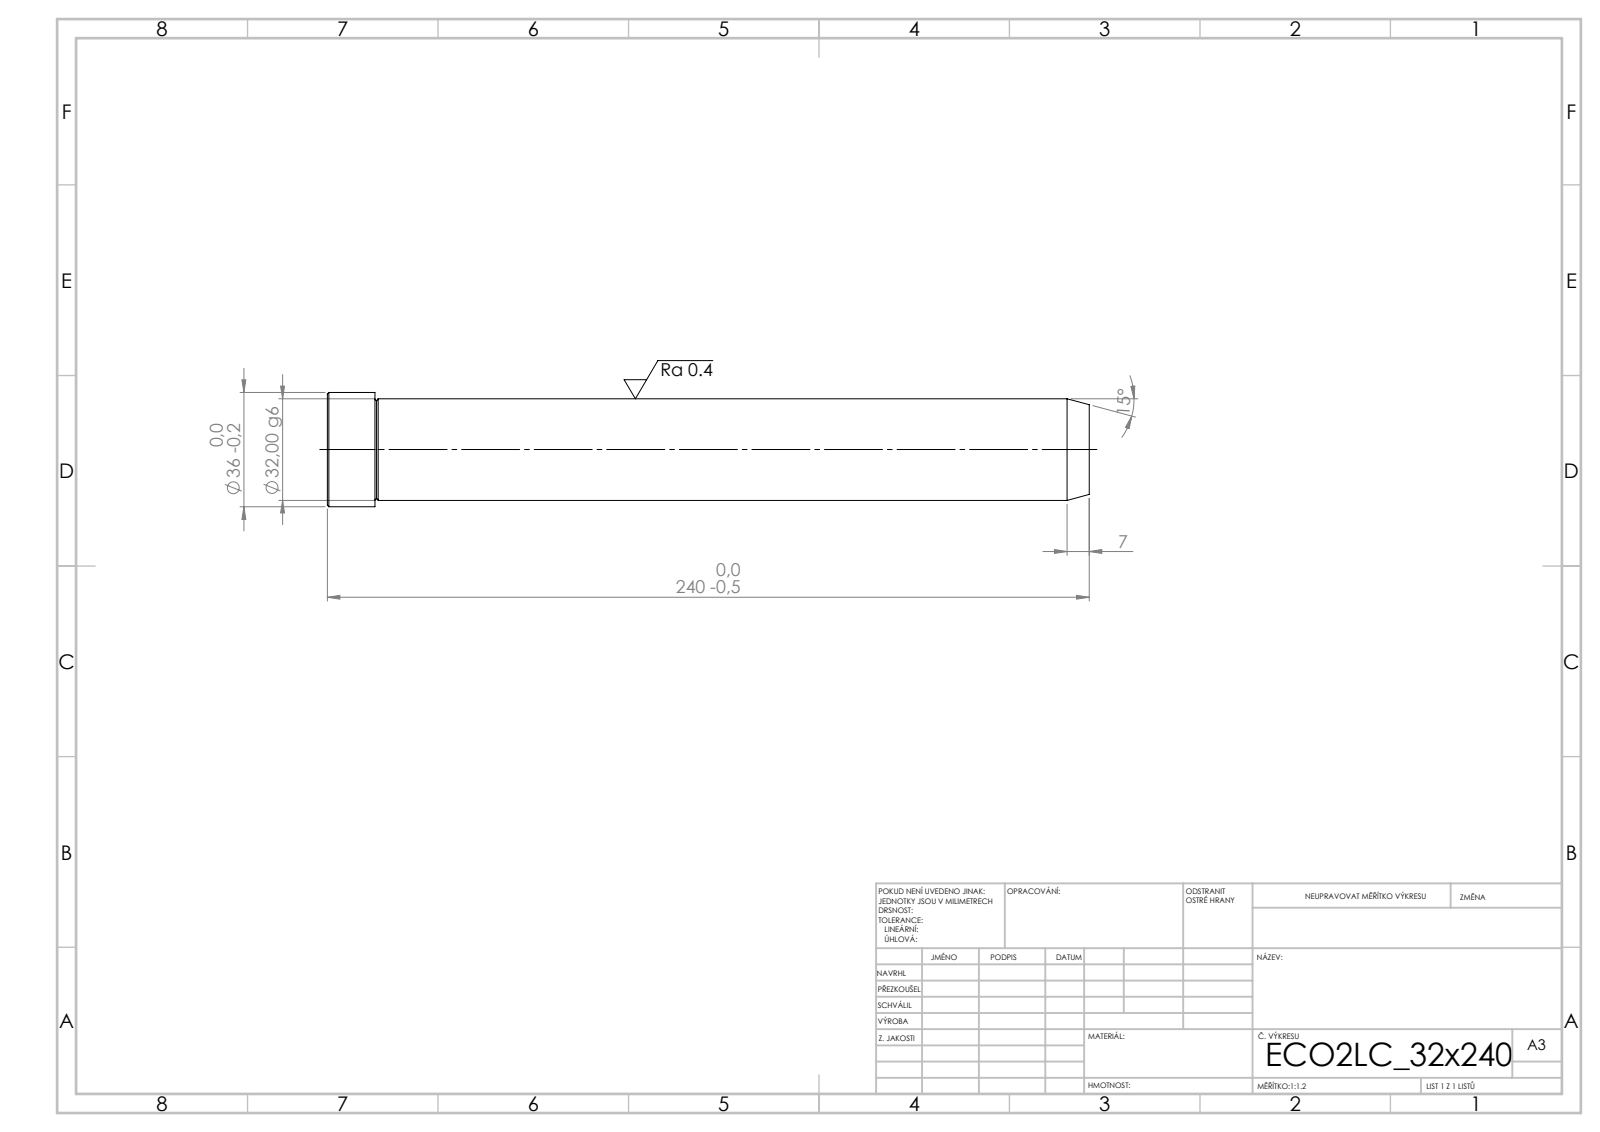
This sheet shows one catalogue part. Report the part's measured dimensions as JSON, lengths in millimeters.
{"step_written_by": "SolidWorks 2019 (CONFIG_CONTROL_DESIGN)", "units": "millimeters", "bodies": {"solids": 1, "faces": 15, "planar": 3, "cylindrical": 4, "other": 8}, "overall_size": [240, 36, 36], "volume_mm3": 195537, "surface_area_mm2": 26177, "round_bosses_or_shafts": [[36, 1], [32, 1]], "face_to_face_distances": [240, 225, 15]}
